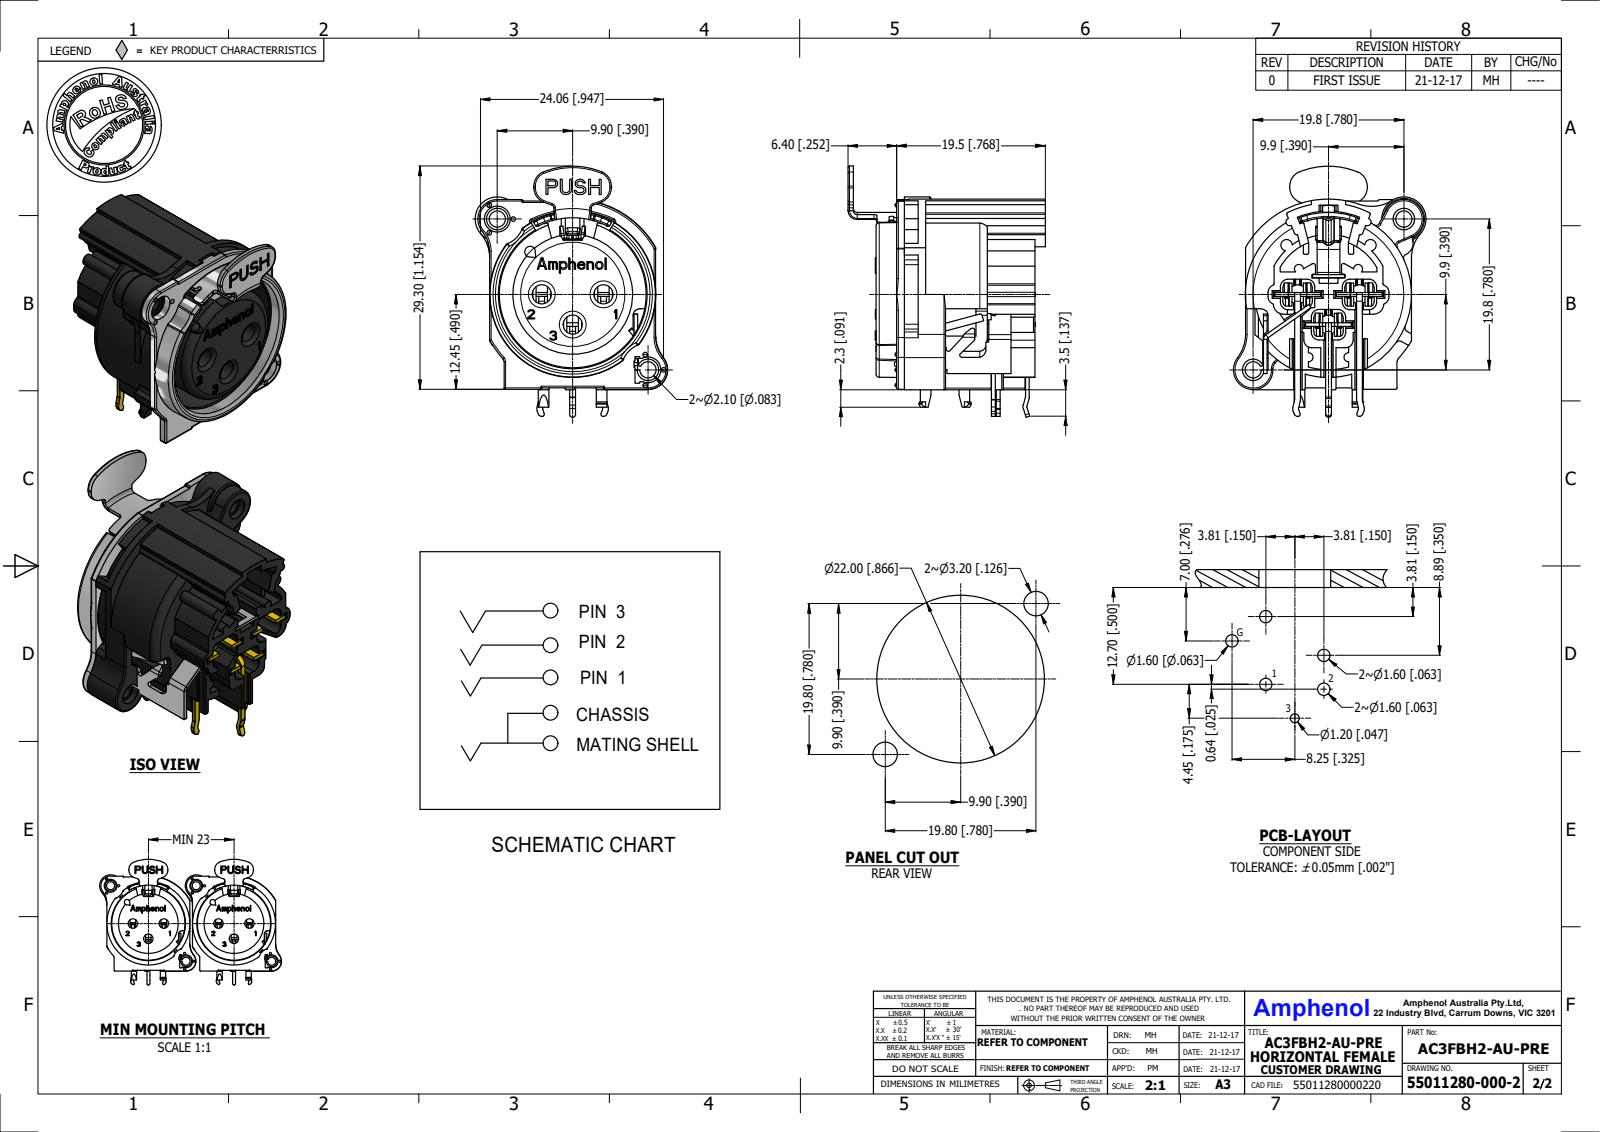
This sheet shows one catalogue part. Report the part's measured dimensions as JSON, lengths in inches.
{"part_name": "AC3FBH2-AU-PRE", "step_written_by": "Autodesk Inventor 2023 (AUTOMOTIVE_DESIGN)", "units": "inches", "bodies": {"solids": 1, "faces": 1840, "planar": 1217, "cylindrical": 401, "other": 222}, "overall_size": [1.293, 1.02, 0.996], "volume_in3": 0.268, "surface_area_in2": 12.72, "round_holes": [[0.098, 3], [0.045, 2], [0.083, 2], [0.11, 2], [0.047, 1], [0.055, 1], [0.134, 1], [0.76, 1], [0.768, 1], [0.813, 1]], "round_bosses_or_shafts": [[0.055, 2], [0.047, 2], [0.858, 1], [0.809, 1], [0.618, 1]], "partial_cylinders_radius": [[0.008, 70], [0.012, 44], [0.02, 30], [0.006, 27], [0.039, 26], [0.024, 21], [0.016, 17], [0.026, 9]], "face_to_face_distances": [0.039, 0.16, 0.069, 0.106, 0.089, 0.067, 0.02, 0.059, 0.146, 0.358], "hole_center_spacings": [0.16, 0.223, 0.452, 0.551, 0.674, 0.115, 0.135, 0.156]}
